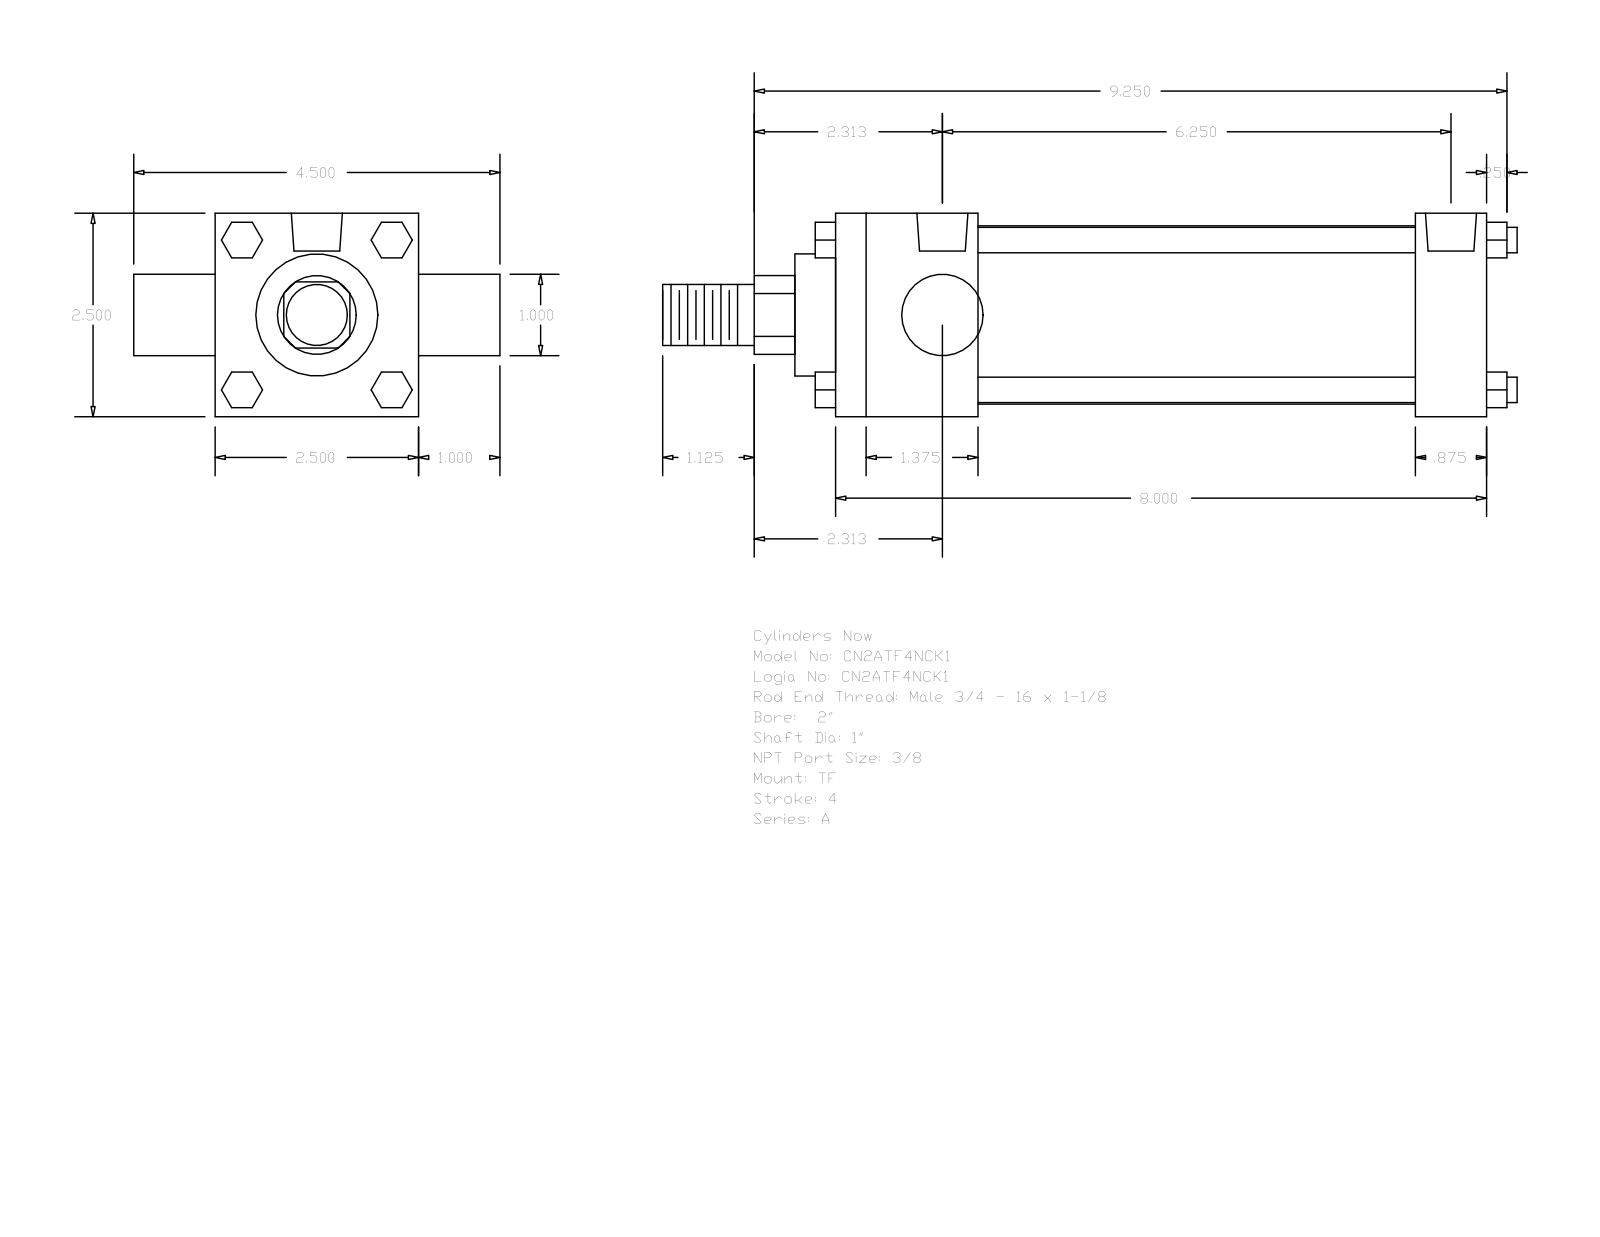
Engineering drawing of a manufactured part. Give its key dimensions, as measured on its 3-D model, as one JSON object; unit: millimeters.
{"part_name": "A_TF__0200_1", "step_written_by": "GSSL Pune (CONFIG_CONTROL_DESIGN)", "units": "millimeters", "bodies": {"solids": 0, "faces": 120, "planar": 92, "cylindrical": 28, "other": 0}, "overall_size": [266.7, 114.3, 63.5], "round_holes": [[5.56, 3], [15.93, 2]], "round_bosses_or_shafts": [[7.94, 4], [25.4, 2], [55.63, 1], [38.1, 1], [19.05, 1]], "partial_cylinders_radius": [[12.29, 1]], "face_to_face_distances": [63.5, 203.2, 44.45, 180.98, 136.53, 158.75, 22.22, 25.4, 88.9, 215.9], "hole_center_spacings": [1.59, 3.98, 153.18, 154.77, 157.16, 158.75]}
